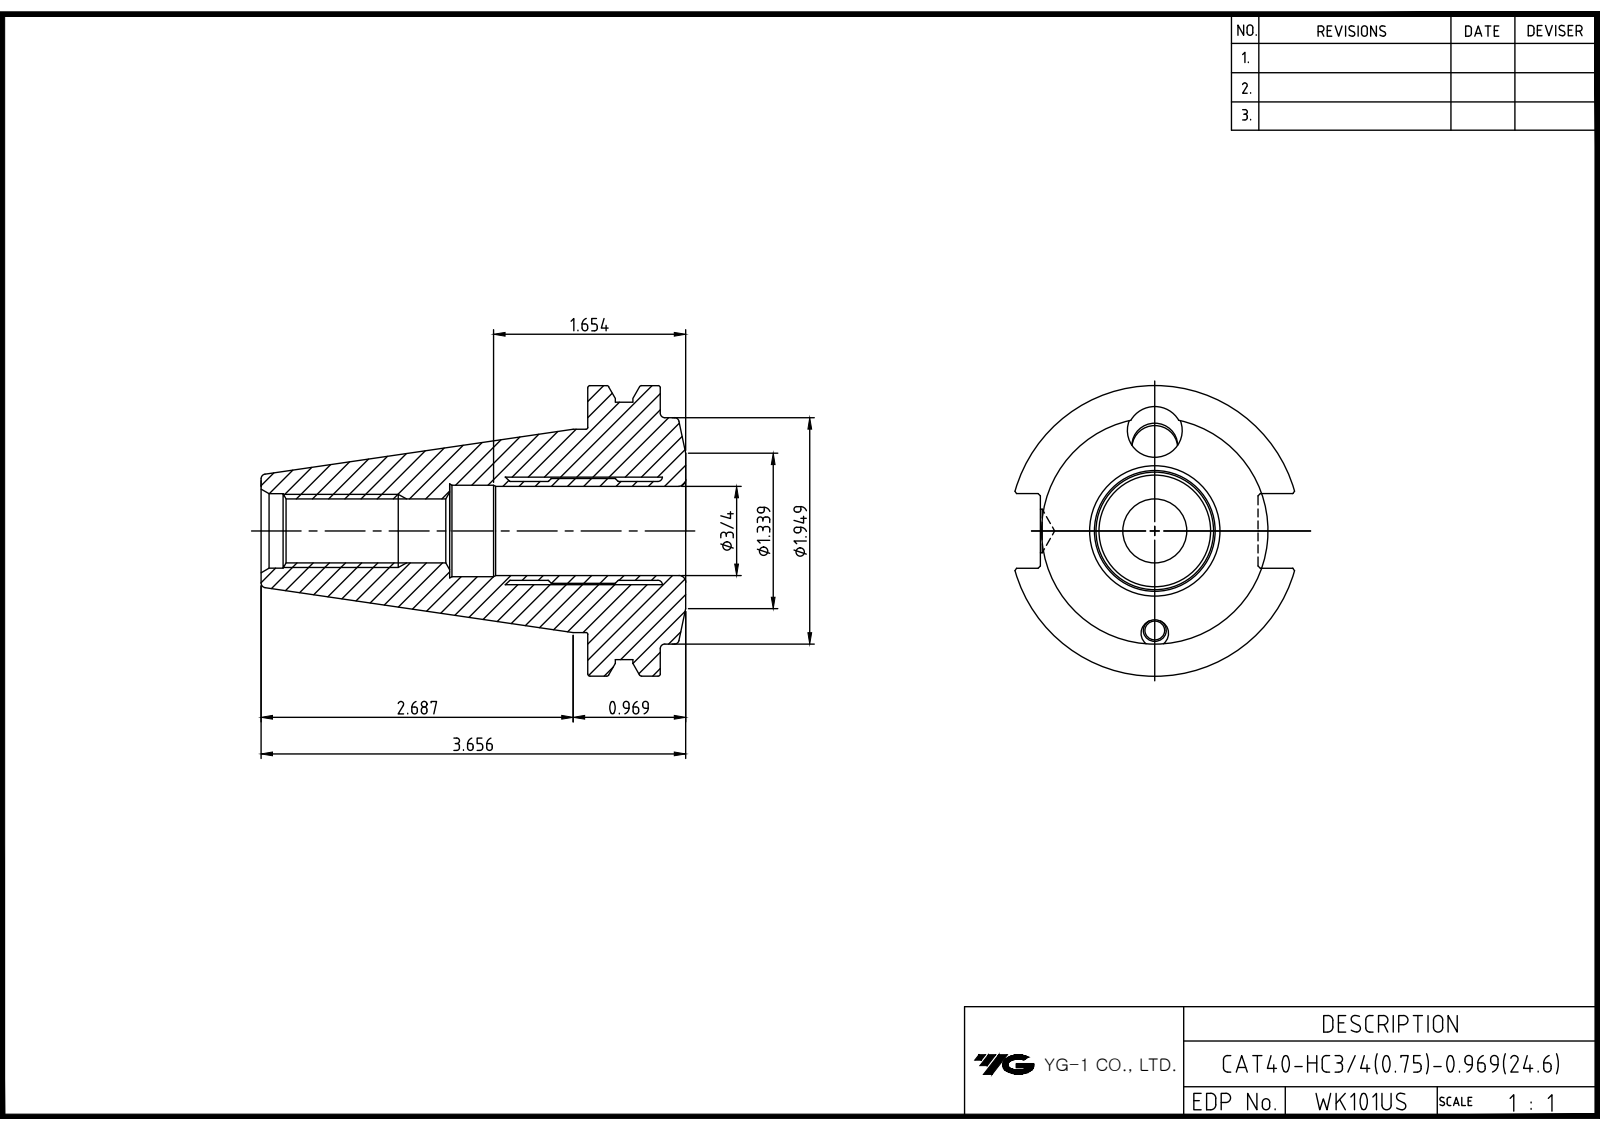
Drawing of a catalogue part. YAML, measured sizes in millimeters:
part_name: "LO-CAT40-HC19.05-24.6"
step_written_by: "Autodesk Inventor 2022 (AUTOMOTIVE_DESIGN)"
units: millimeters
bodies: {solids: 1, faces: 53, planar: 25, cylindrical: 12, other: 16}
overall_size: [92.85, 63.5, 61.09]
volume: 102011
surface_area: 21609
round_holes:
  - {diameter: 9.53, count: 1}
  - {diameter: 13.39, count: 1}
  - {diameter: 16.3, count: 1}
  - {diameter: 19.05, count: 1}
round_bosses_or_shafts:
  - {diameter: 63.5, count: 1}
  - {diameter: 56.3, count: 1}
  - {diameter: 49.5, count: 1}
  - {diameter: 44.45, count: 1}
face_to_face_distances: [15.88, 21.43, 5.55, 47.6, 16.38, 71.42, 87.3, 92.85, 41.45, 29.97]
